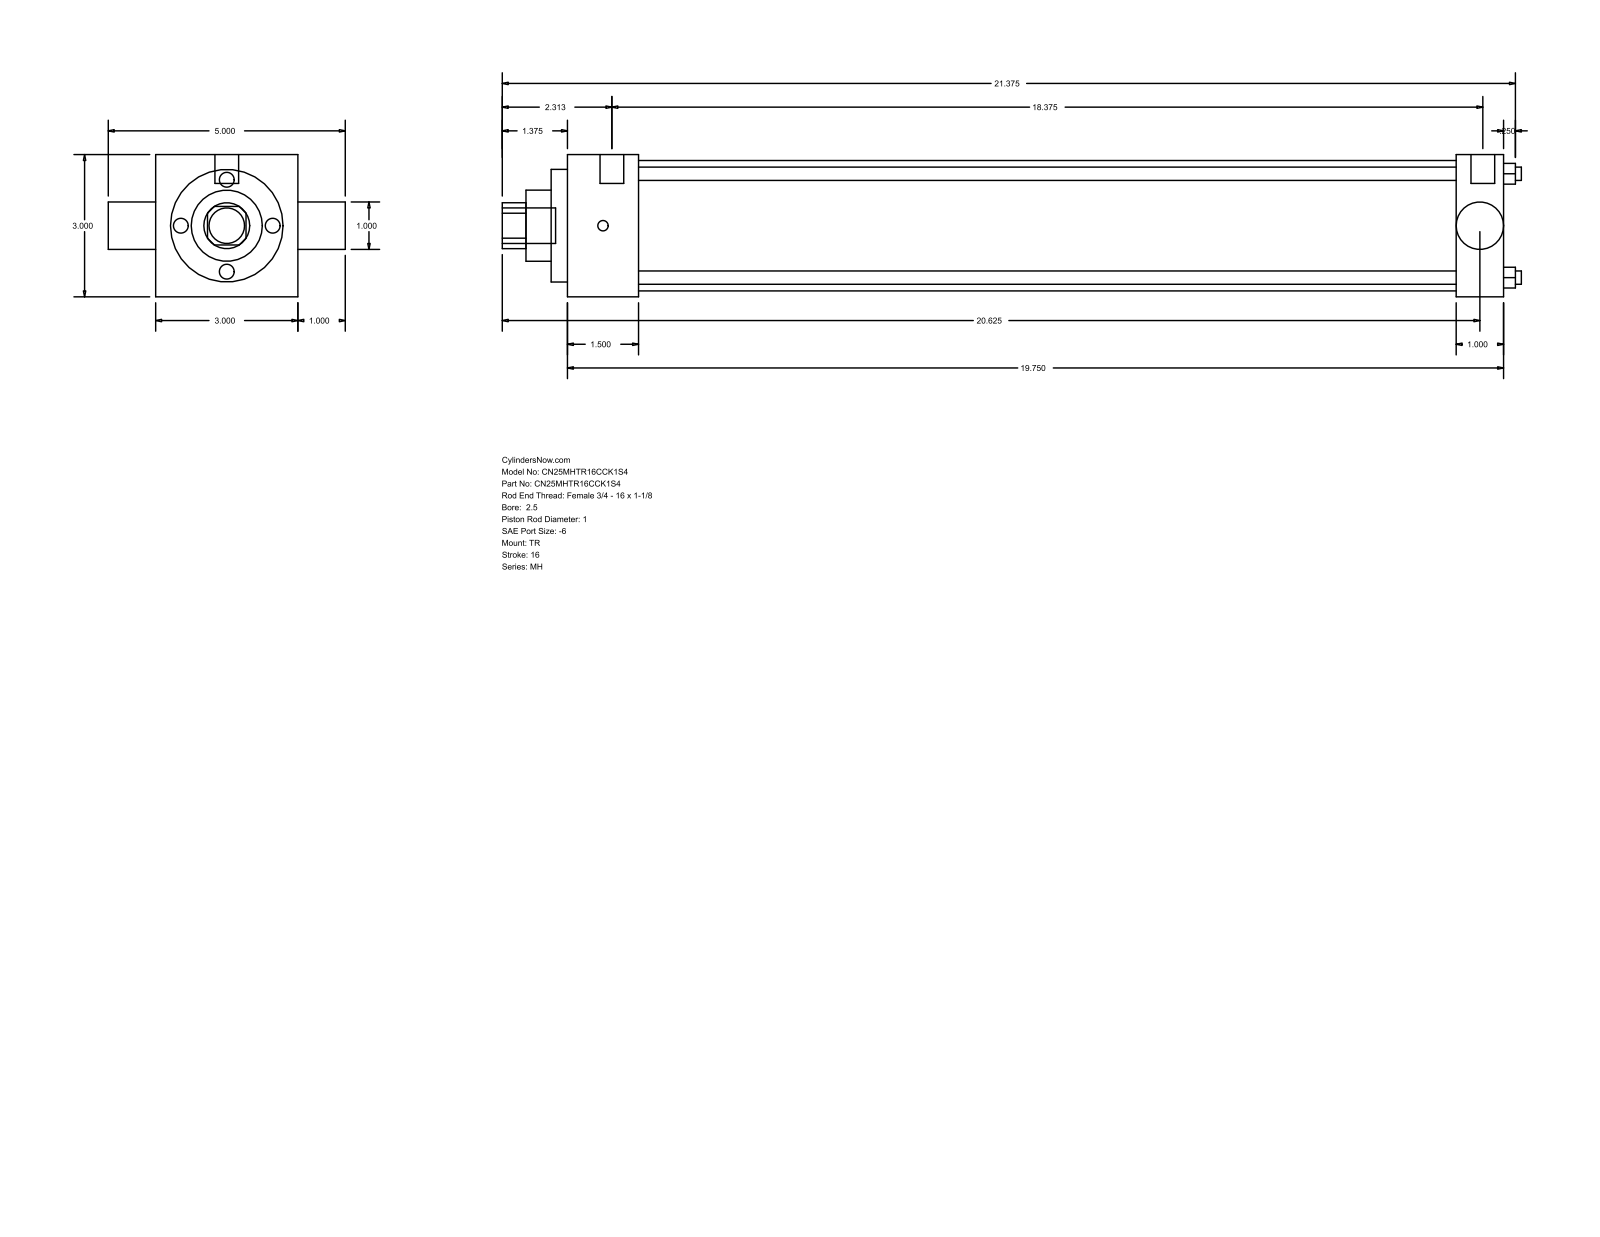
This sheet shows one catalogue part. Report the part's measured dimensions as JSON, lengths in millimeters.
{"part_name": "MH_TR__0250_1", "step_written_by": "GSSL Pune (CONFIG_CONTROL_DESIGN)", "units": "millimeters", "bodies": {"solids": 0, "faces": 86, "planar": 61, "cylindrical": 25, "other": 0}, "overall_size": [546.1, 127, 76.2], "round_holes": [[7.14, 4], [25.35, 1], [25.4, 1], [38.1, 1], [60.33, 1], [69.85, 1]], "round_bosses_or_shafts": [[5.56, 3], [12.7, 2], [19.05, 1]], "partial_cylinders_radius": [[12.29, 1]], "face_to_face_distances": [76.2, 501.66, 25.4, 38.11, 463.55, 476.26, 438.15, 8.73, 46.84, 484.99], "hole_center_spacings": [39.33, 55.62, 78.66]}
